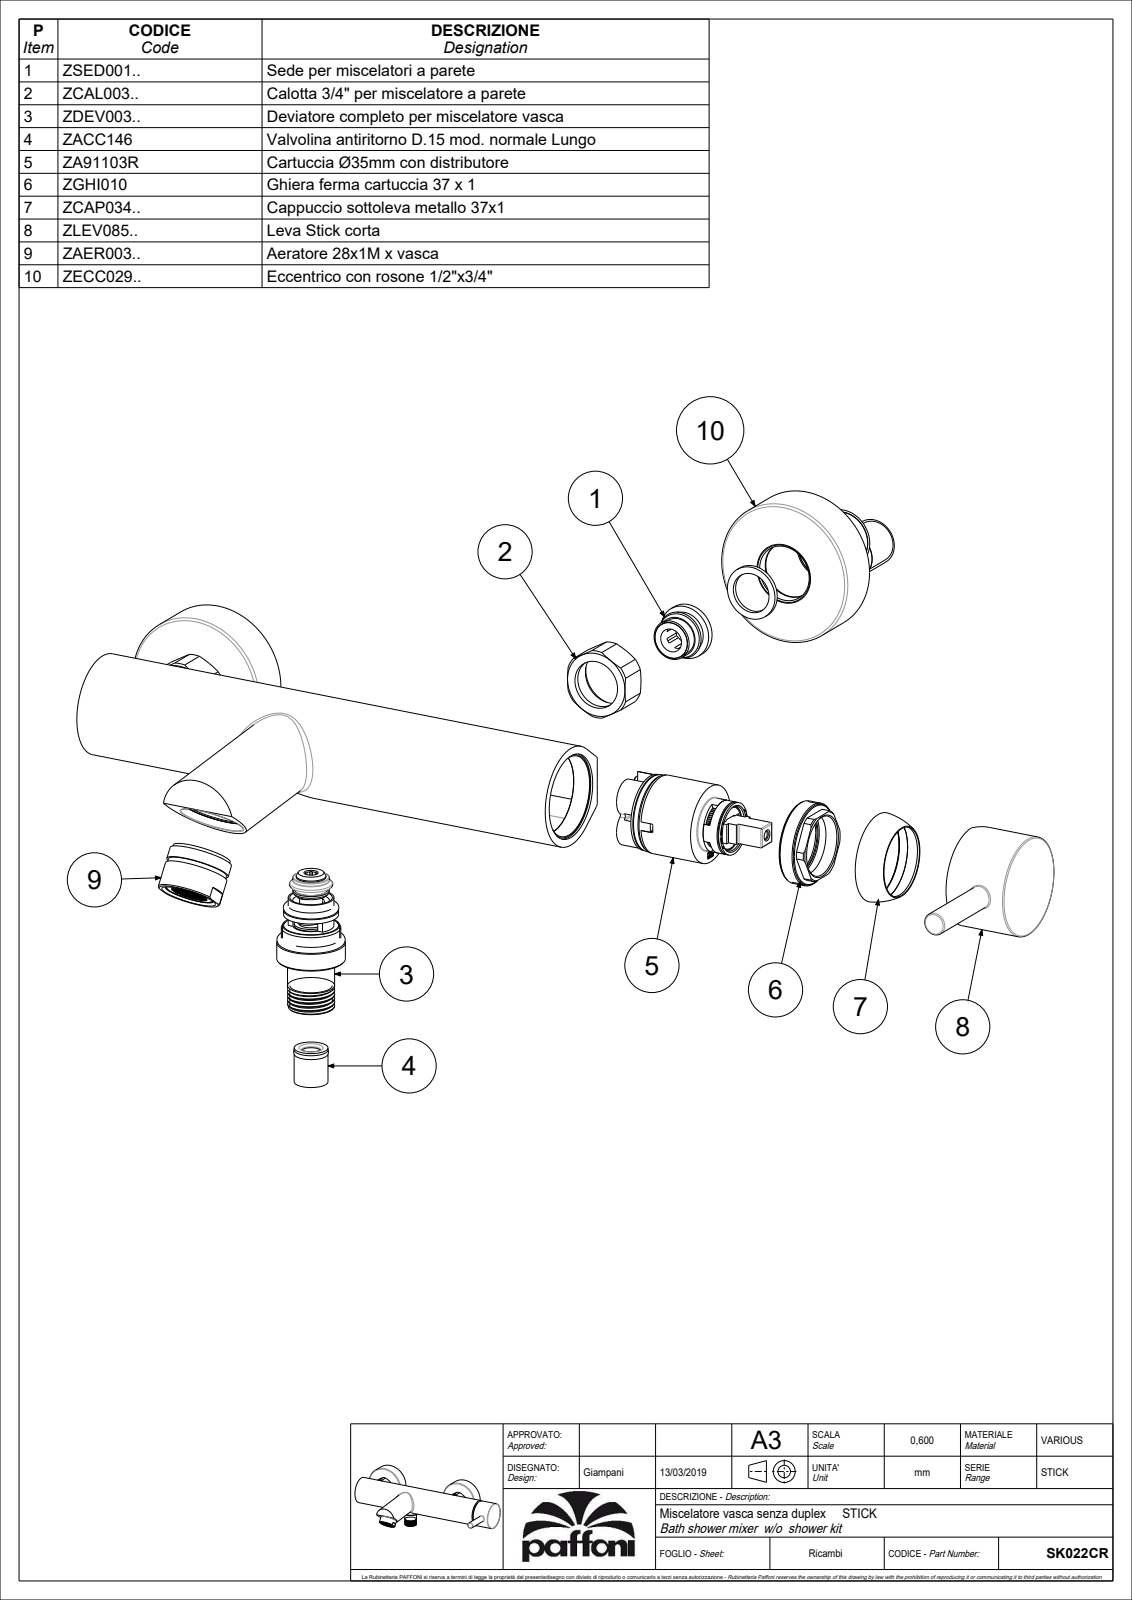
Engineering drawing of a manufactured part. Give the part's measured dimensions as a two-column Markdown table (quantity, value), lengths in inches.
| quantity | value |
| --- | --- |
| part name | SK022CR |
| STEP written by | CREO PARAMETRIC BY PTC INC, 2020044 (CONFIG_CONTROL_DESIGN) |
| units | inches |
| bodies | 1 solid, 297 faces (70 planar, 95 cylindrical, 132 other) |
| overall size | 10.86 × 6 × 3.081 |
| volume | 39.41 in³ |
| surface area | 130.5 in² |
| round holes (diameter × count) | 0.689 × 2, 0.748 × 2, 0.866 × 2, 0.118 × 1, 1.22 × 1 |
| round bosses / shafts (diameter × count) | 2.539 × 2, 0.63 × 2, 1.752 × 1, 1.39 × 1, 1.181 × 1, 1.102 × 1, 0.811 × 1, 0.394 × 1 |
| partial cylindrical surfaces (radius × count) | 0.02 × 8, 0.059 × 2, 0.61 × 2, 0.886 × 1 |
| main face-to-face distances | 0.787, 1.398, 0.61, 1.142, 0.059, 10.382, 0.551, 1.339, 2.953, 9.823 |
| hole center spacings | 3.197, 5.906, 9.102 |
